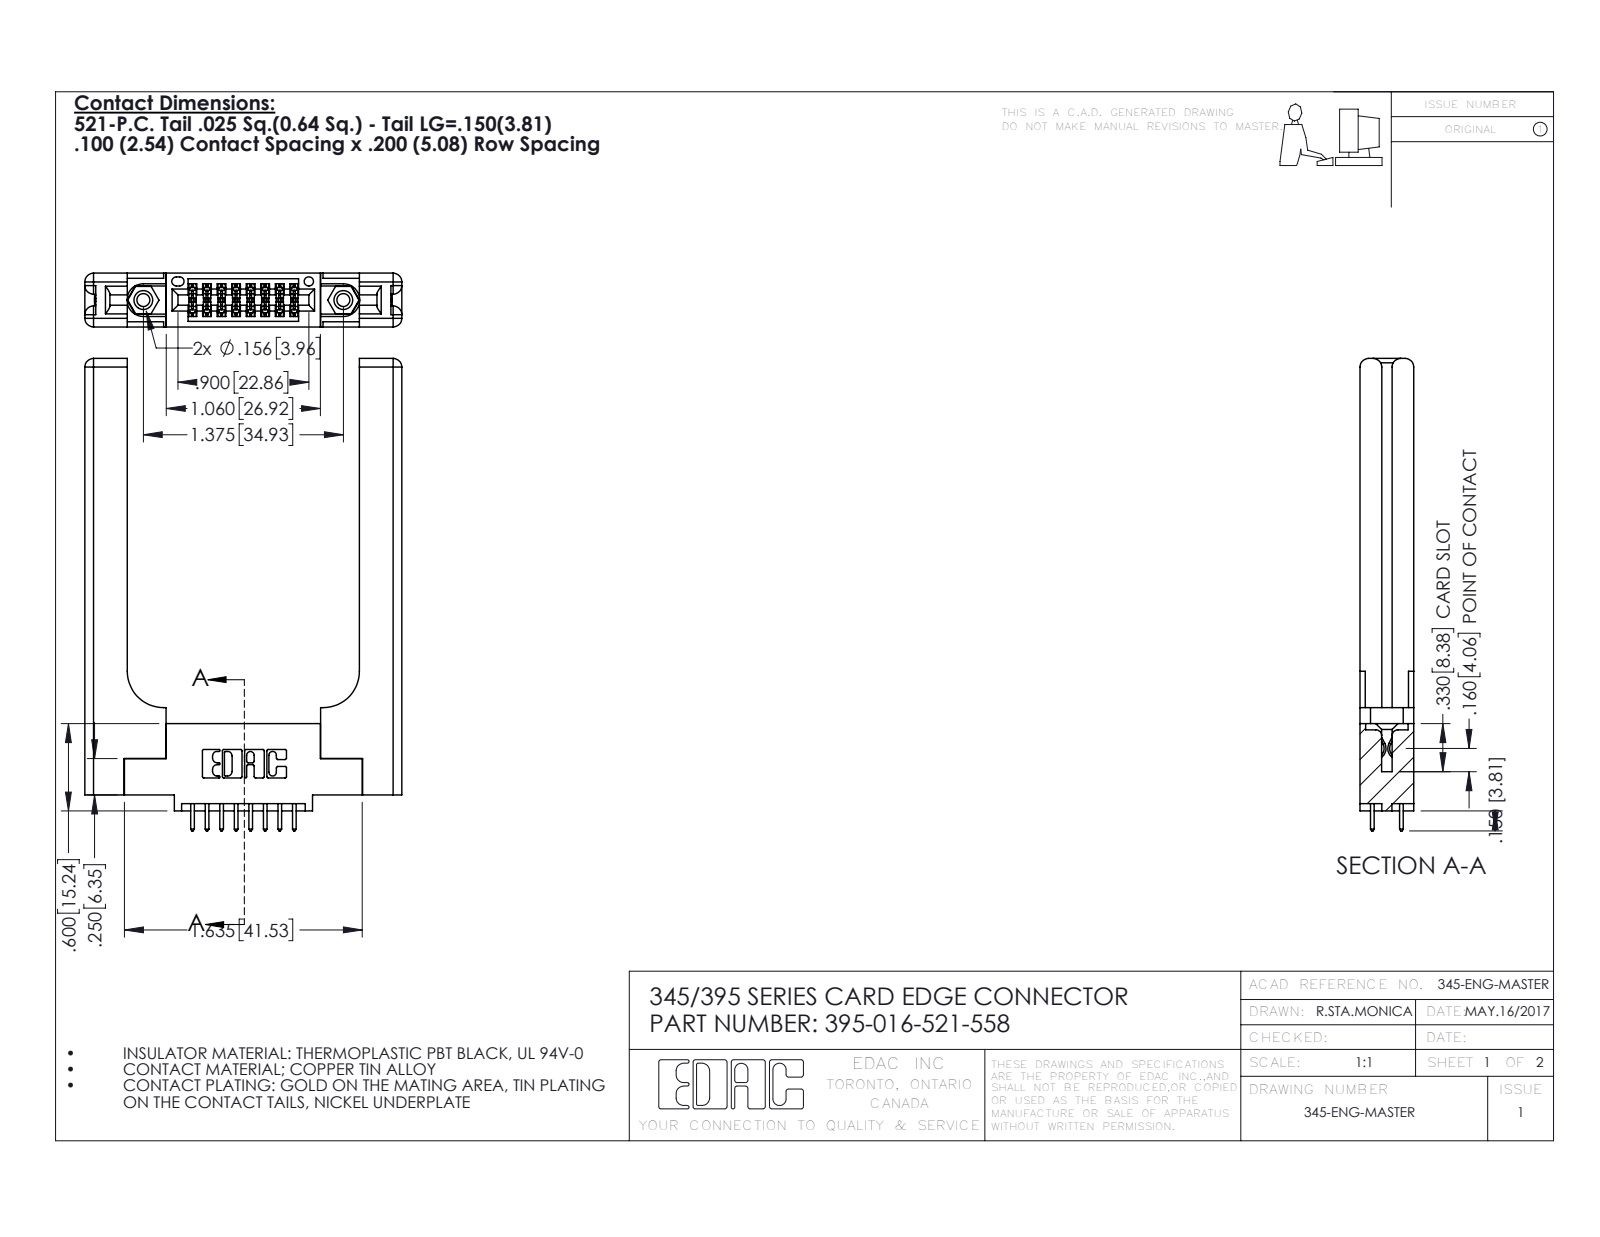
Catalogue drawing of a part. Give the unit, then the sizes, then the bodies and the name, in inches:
Units: inches
Overall size (bounding box): 3.247 × 2.179 × 0.37
Round holes (diameter × count): ⌀0.089 ×2, ⌀0.125 ×2, ⌀0.156 ×2, ⌀0.064 ×1
Round bosses / shafts (diameter × count): ⌀0.155 ×2
Partial cylindrical surfaces — rounded edges, fillets, slot ends (radius × count): R0.006 ×24, R0.01 ×22, R0.01 ×16, R0.06 ×16, R0.007 ×6, R0.031 ×6, R0.026 ×3, R0.014 ×2
Main face-to-face distances: 0.37, 0.15, 0.072, 0.22, 0.148, 0.077, 0.298, 1.596, 0.071, 0.225
Hole centre spacings: 0.27, 1.144, 1.375
Volume: 0.821 in³ · Surface area: 18.31 in²
Bodies: 21 solids, 1186 faces (760 planar, 366 cylindrical, 60 other)
Part name (STEP PRODUCT): 395-016-521-558; 345-250-001_345-250-001-102; 345-220-058_345-220-058; 345 Part_0.110 Offset - 0.156 Dia-TH (+1 more)
STEP written by: SolidWorks 2016 (CONFIG_CONTROL_DESIGN)
